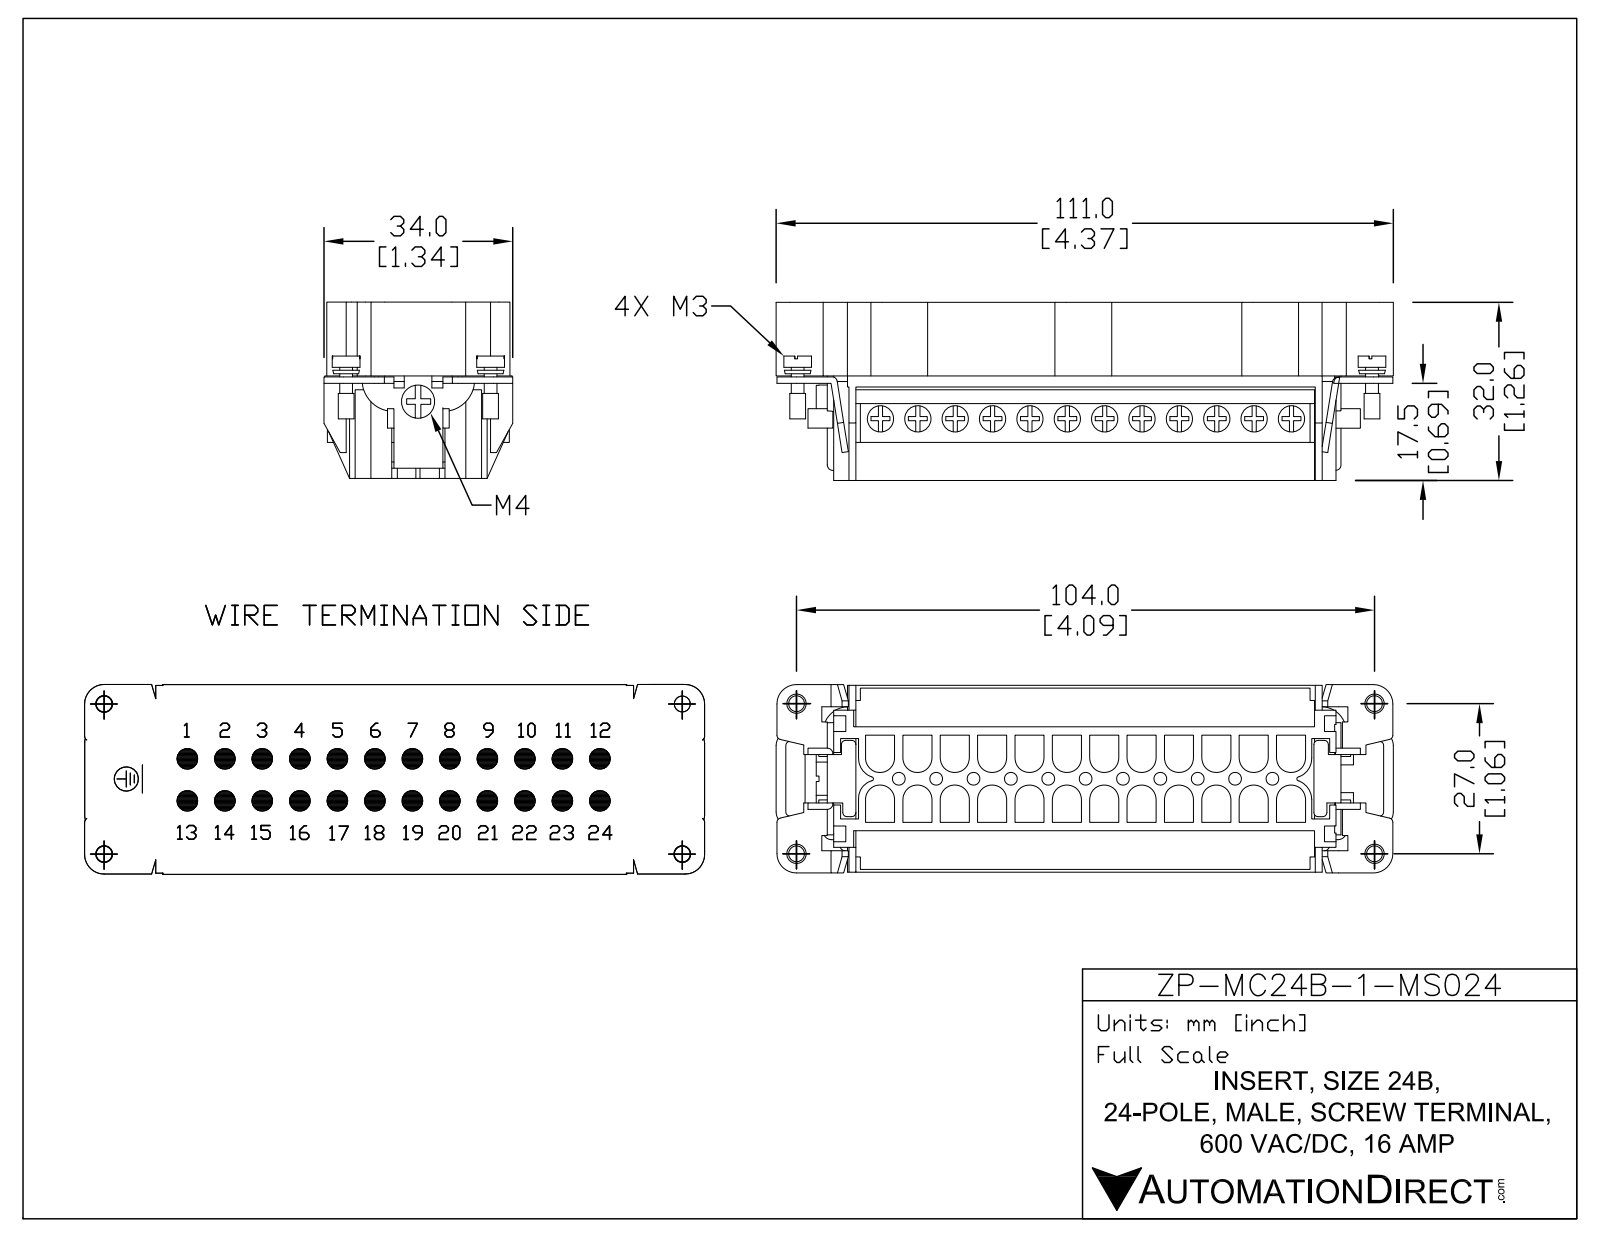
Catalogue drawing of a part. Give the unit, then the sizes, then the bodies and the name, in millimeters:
Units: millimetres
Overall size (bounding box): 111.5 × 34 × 32.25
Round holes (diameter × count): ⌀4.75 ×12, ⌀2.3 ×11, ⌀3.5 ×4, ⌀3 ×1
Round bosses / shafts (diameter × count): ⌀2.5 ×24, ⌀5 ×4, ⌀2.85 ×4, ⌀2.3 ×4, ⌀6 ×1
Partial cylindrical surfaces — rounded edges, fillets, slot ends (radius × count): R0.75 ×24, R2.62 ×24, R2.62 ×24, R1 ×11, R0.25 ×10, R2 ×10, R2.5 ×4, R2.5 ×4
Main face-to-face distances: 2.5, 7, 1.75, 12, 24.25, 5, 13.5, 3.63, 1.88, 20.62
Hole centre spacings: 6.75, 13.5, 20.25, 27, 33.75, 40.5, 47.25, 54
Volume: 42 809 mm³ · Surface area: 48 858 mm²
Bodies: 8 solids, 838 faces (576 planar, 210 cylindrical, 52 other)
Part name (STEP PRODUCT): ZP-24B-24-MS-INSERT
STEP written by: SolidWorks 2011 (AUTOMOTIVE_DESIGN)
